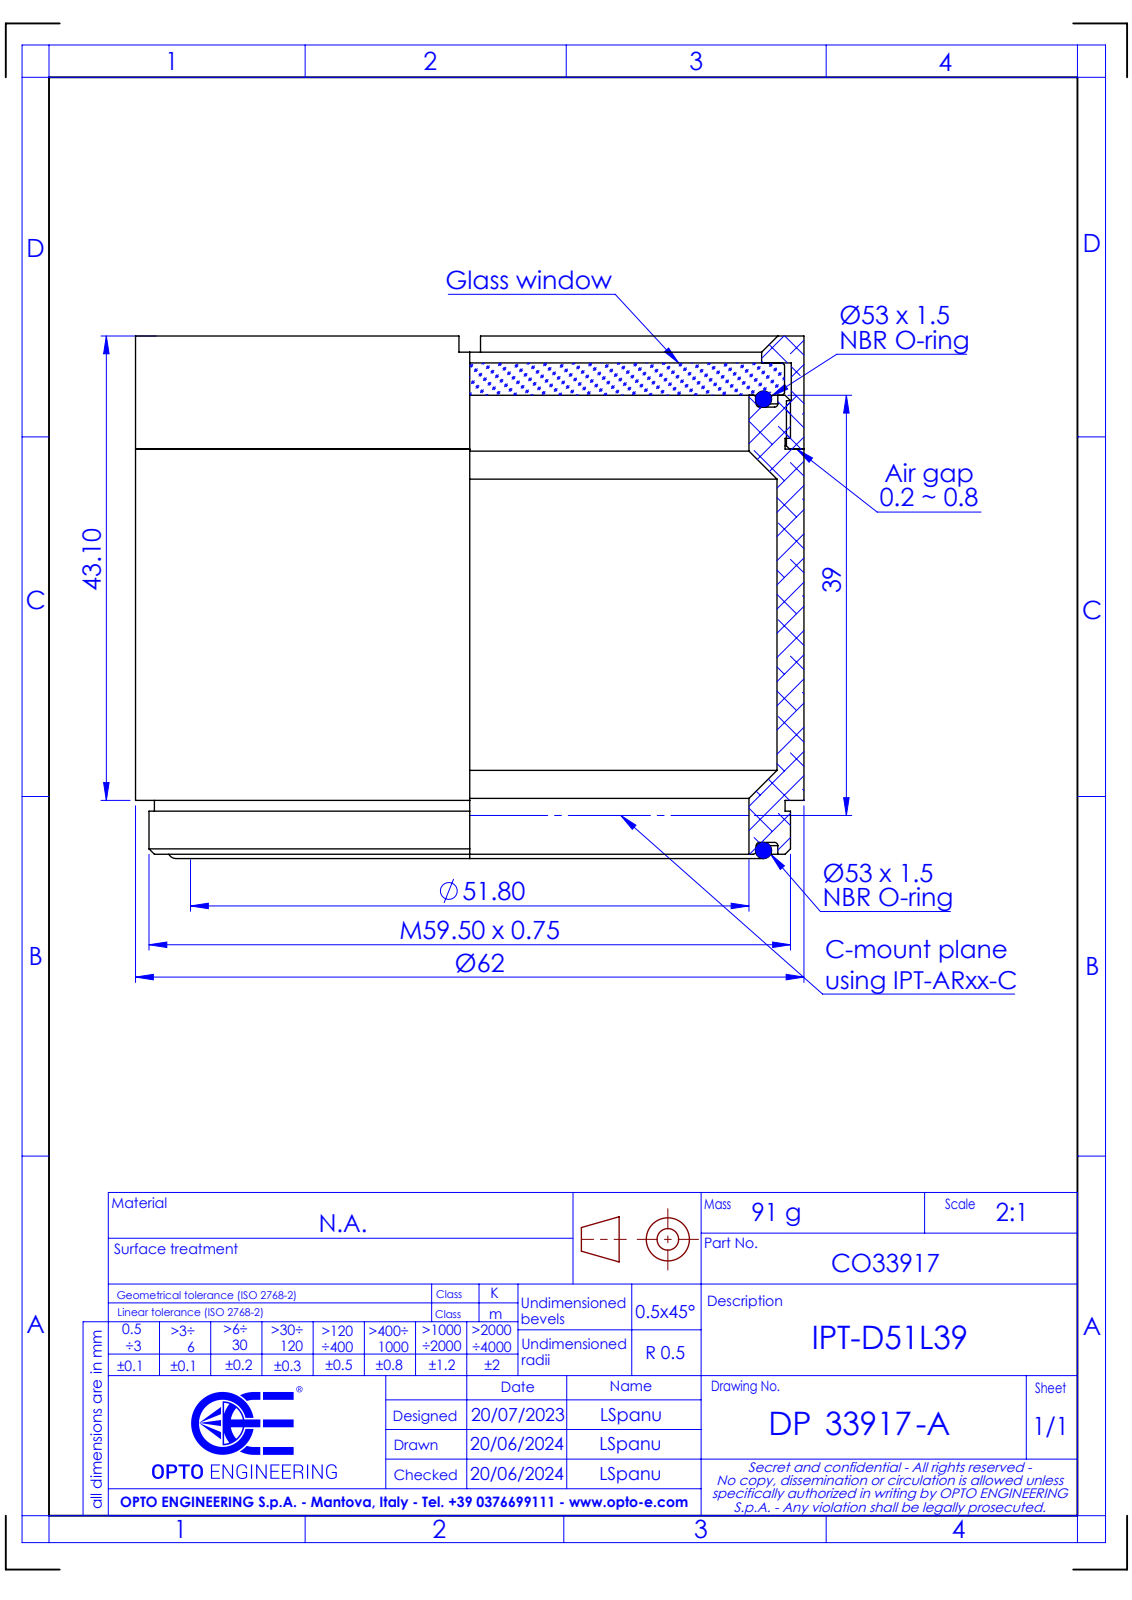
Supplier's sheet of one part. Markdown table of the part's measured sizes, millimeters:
| quantity | value |
| --- | --- |
| part name | DP33917-A_IPT-D51L39 |
| STEP written by | SolidWorks 2021 (CONFIG_CONTROL_DESIGN) |
| units | millimeters |
| bodies | 0 solids, 48 faces (16 planar, 16 cylindrical, 16 other) |
| overall size | 62 × 62 × 48.5 |
| round holes (diameter × count) | 51.8 × 1, 54.15 × 1, 57 × 1, 57.15 × 1 |
| round bosses / shafts (diameter × count) | 62 × 1, 59.5 × 1, 58.5 × 1 |
| main face-to-face distances | 8, 10.5, 2.5, 32.6, 40.6, 43.1, 3.9, 36.5, 44.5, 47 |
